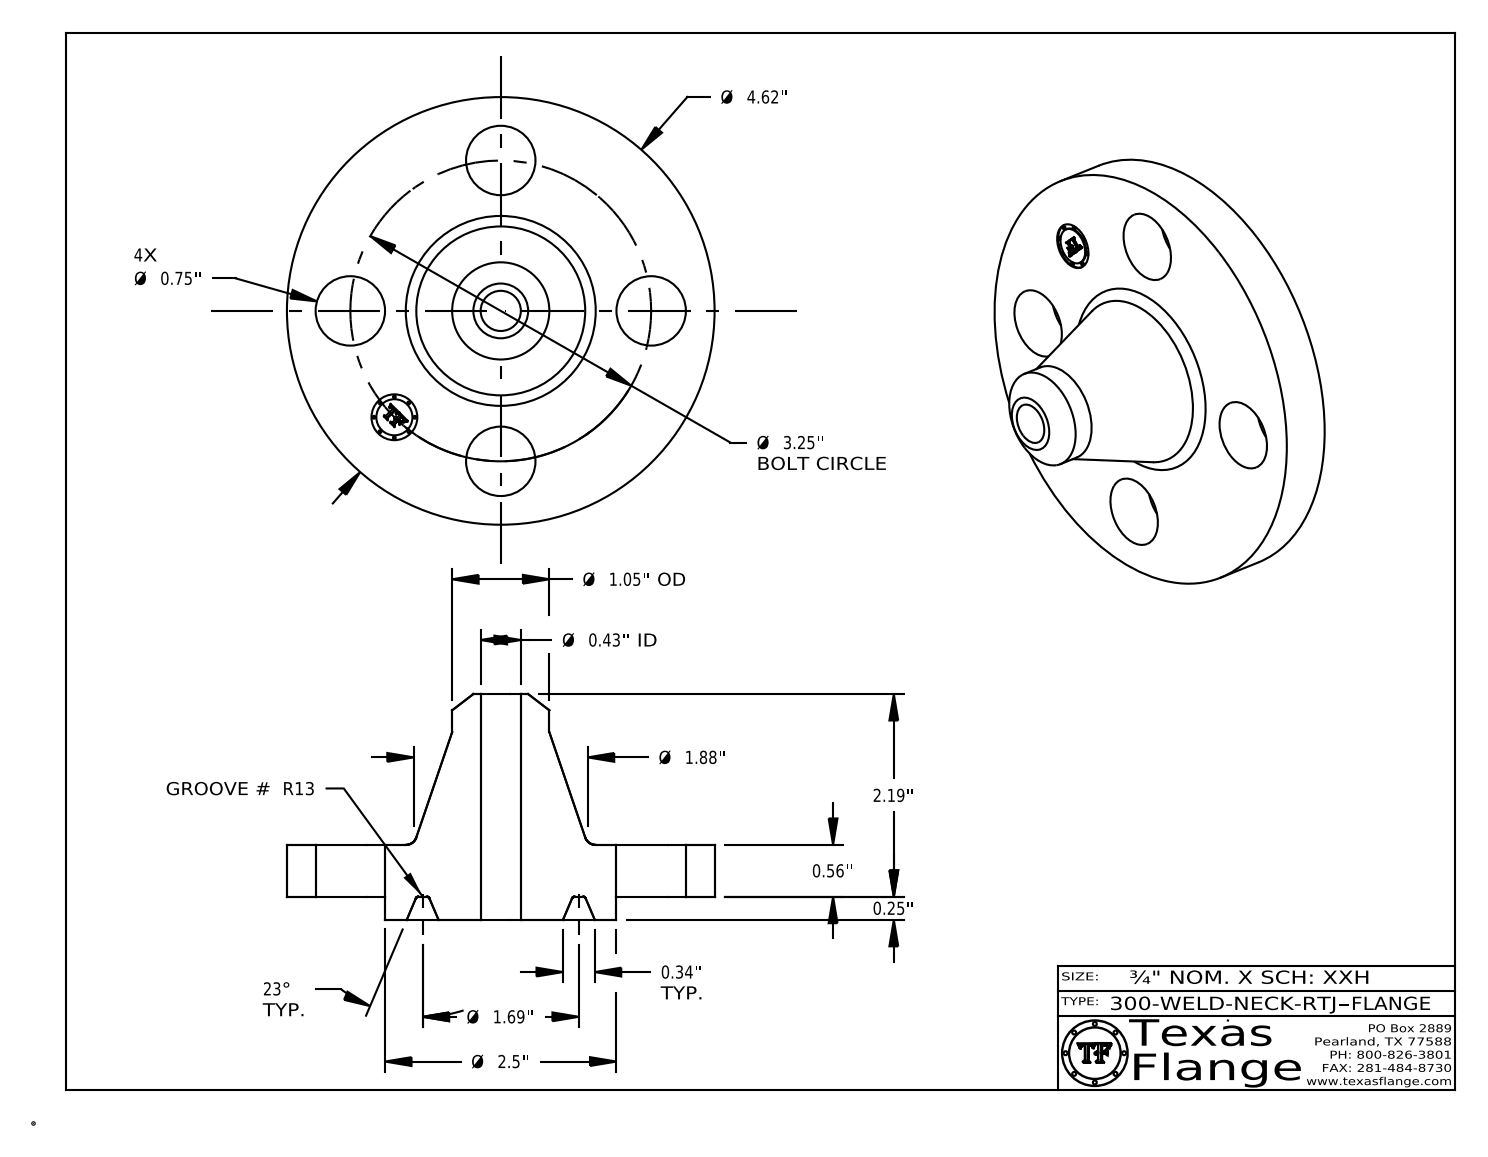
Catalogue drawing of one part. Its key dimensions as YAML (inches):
part_name: "300-WELD-NECK-RTJ"
step_written_by: "CATIA V5 STEP AP214 (AUTOMOTIVE_DESIGN)"
units: inches
bodies: {solids: 1, faces: 421, planar: 371, cylindrical: 36, other: 14}
overall_size: [4.62, 4.62, 2.44]
volume: 11.36
surface_area: 55.01
round_holes:
  - {diameter: 0.75, count: 4}
  - {diameter: 0.434, count: 1}
  - {diameter: 0.495, count: 1}
round_bosses_or_shafts:
  - {diameter: 0.03, count: 8}
  - {diameter: 4.62, count: 1}
  - {diameter: 2.5, count: 1}
  - {diameter: 1.05, count: 1}
  - {diameter: 0.39, count: 1}
face_to_face_distances: [0.56, 0.25, 0.81, 2.44, 2.19, 1.63, 0.795, 0.545, 0.015, 1.645]
hole_center_spacings: [1.625, 2.298, 1.244, 3.003, 3.25]
